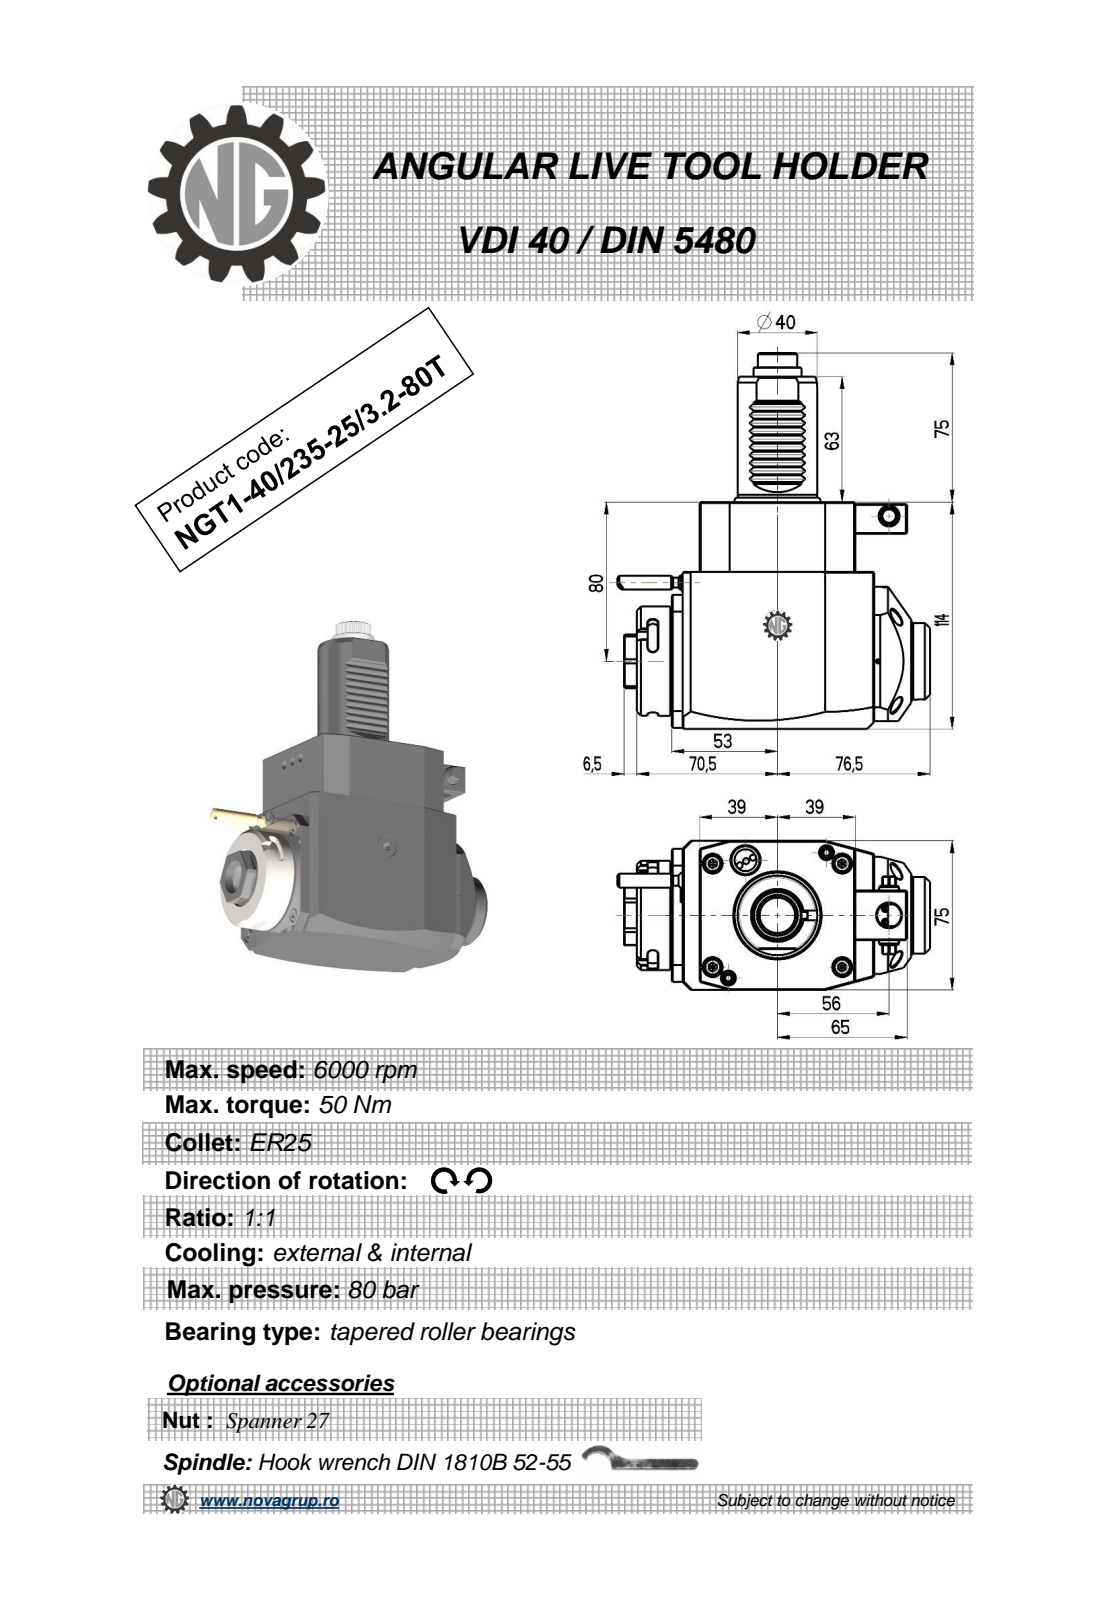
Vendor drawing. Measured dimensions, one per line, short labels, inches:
name: NGT1_40_235_25_3_2_80T
written by: PRO/ENGINEER BY PARAMETRIC TECHNOLOGY CORPORATION, 2010280 (CONFIG_CONTROL_DESIGN)
unit: in
bodies: 1 solid, 462 faces (186 planar, 180 cylindrical, 96 other)
size: 7.441 × 6.174 × 2.953
volume: 59.23 in³; area: 111.6 in²
holes: 1× ⌀0.098, 1× ⌀0.118, 1× ⌀0.374, 1× ⌀0.472, 1× ⌀0.709
bosses: 2× ⌀0.315, 1× ⌀2.165, 1× ⌀1.89, 1× ⌀1.575, 1× ⌀1.516, 1× ⌀0.945, 1× ⌀0.394, 1× ⌀0.276
rounds: 48× R0.082, 10× R0.012, 6× R0.098, 2× R0.591, 2× R7.087, 1× R0.152, 1× R0.167, 1× R0.357
face distances: 2.953, 4.488, 0.551, 4.311, 3.622, 3.071, 0.689, 1.24, 3.11, 1.378
hole spacings: 1.436, 1.701, 2.815
